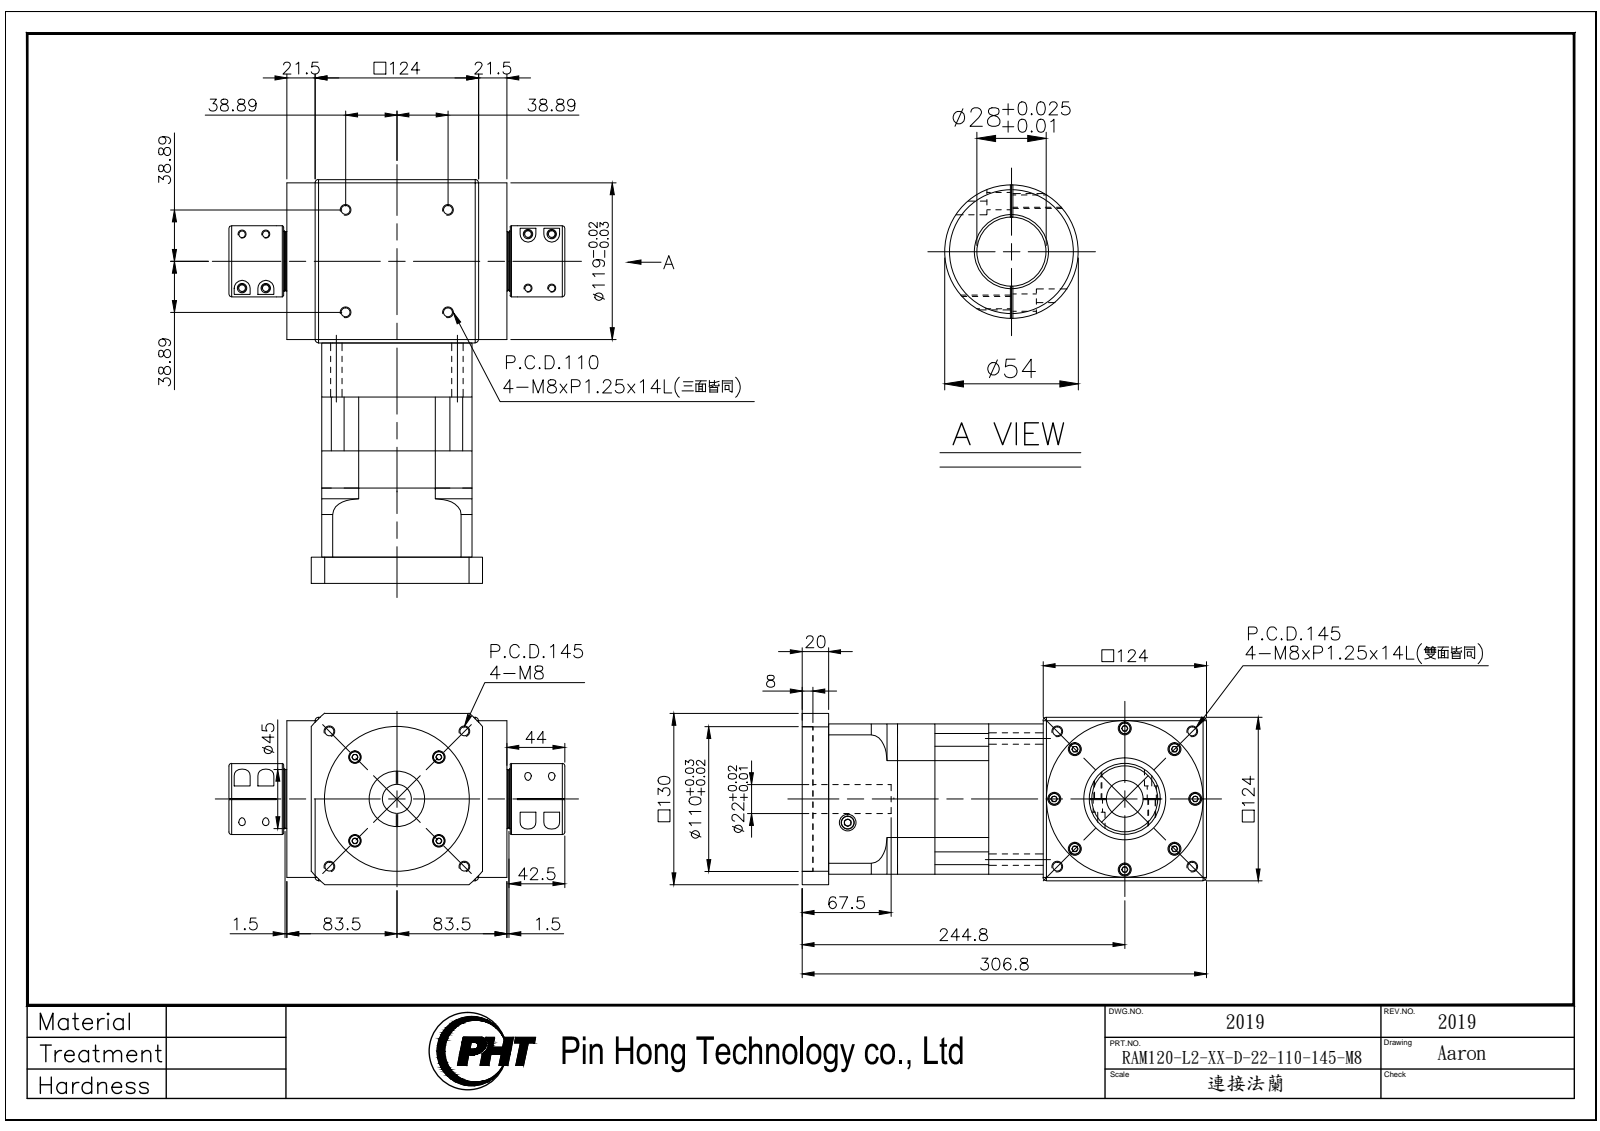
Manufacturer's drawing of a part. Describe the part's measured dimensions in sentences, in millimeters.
The part is named "RAM120-L2-XX-D-22-110-145-M8_2019". Its 3-D file was written by "SolidWorks 2016 (AUTOMOTIVE_DESIGN)". It is 5 solids with 1290 faces: 640 planar, 426 cylindrical and 224 other. Overall it measures 306.8 by 255 by 130 millimeters. Its volume is 4 487 000 cubic millimeters and its surface area 428 100 square millimeters. Round holes: 16 of diameter 6.8, 12 of diameter 9.5, 8 of diameter 5.3, 8 of diameter 7, 8 of diameter 9, 8 of diameter 14, 4 of diameter 4.2, 4 of diameter 5.5, 4 of diameter 8.6, 2 of diameter 12.7, 1 of diameter 22, 1 of diameter 28. Round bosses or shafts: 12 of diameter 13, 8 of diameter 10.5, 8 of diameter 10, 8 of diameter 6, 4 of diameter 8.5, 1 of diameter 119, 1 of diameter 62, 1 of diameter 54. Partial cylindrical surfaces (rounded edges, fillets, slot ends): 8 of radius 3.52, 8 of radius 5.5, 4 of radius 7, 1 of radius 64, 1 of radius 75, 1 of radius 85, 1 of radius 86.2. The main face-to-face distances are 5, 119, 124, 114, 69.5, 28.3, 41.2, 3, 41, 110.5. The hole center spacings are 59, 10, 15.4, 17.24, 19.42, 21.77, 39.8, 51.28.
